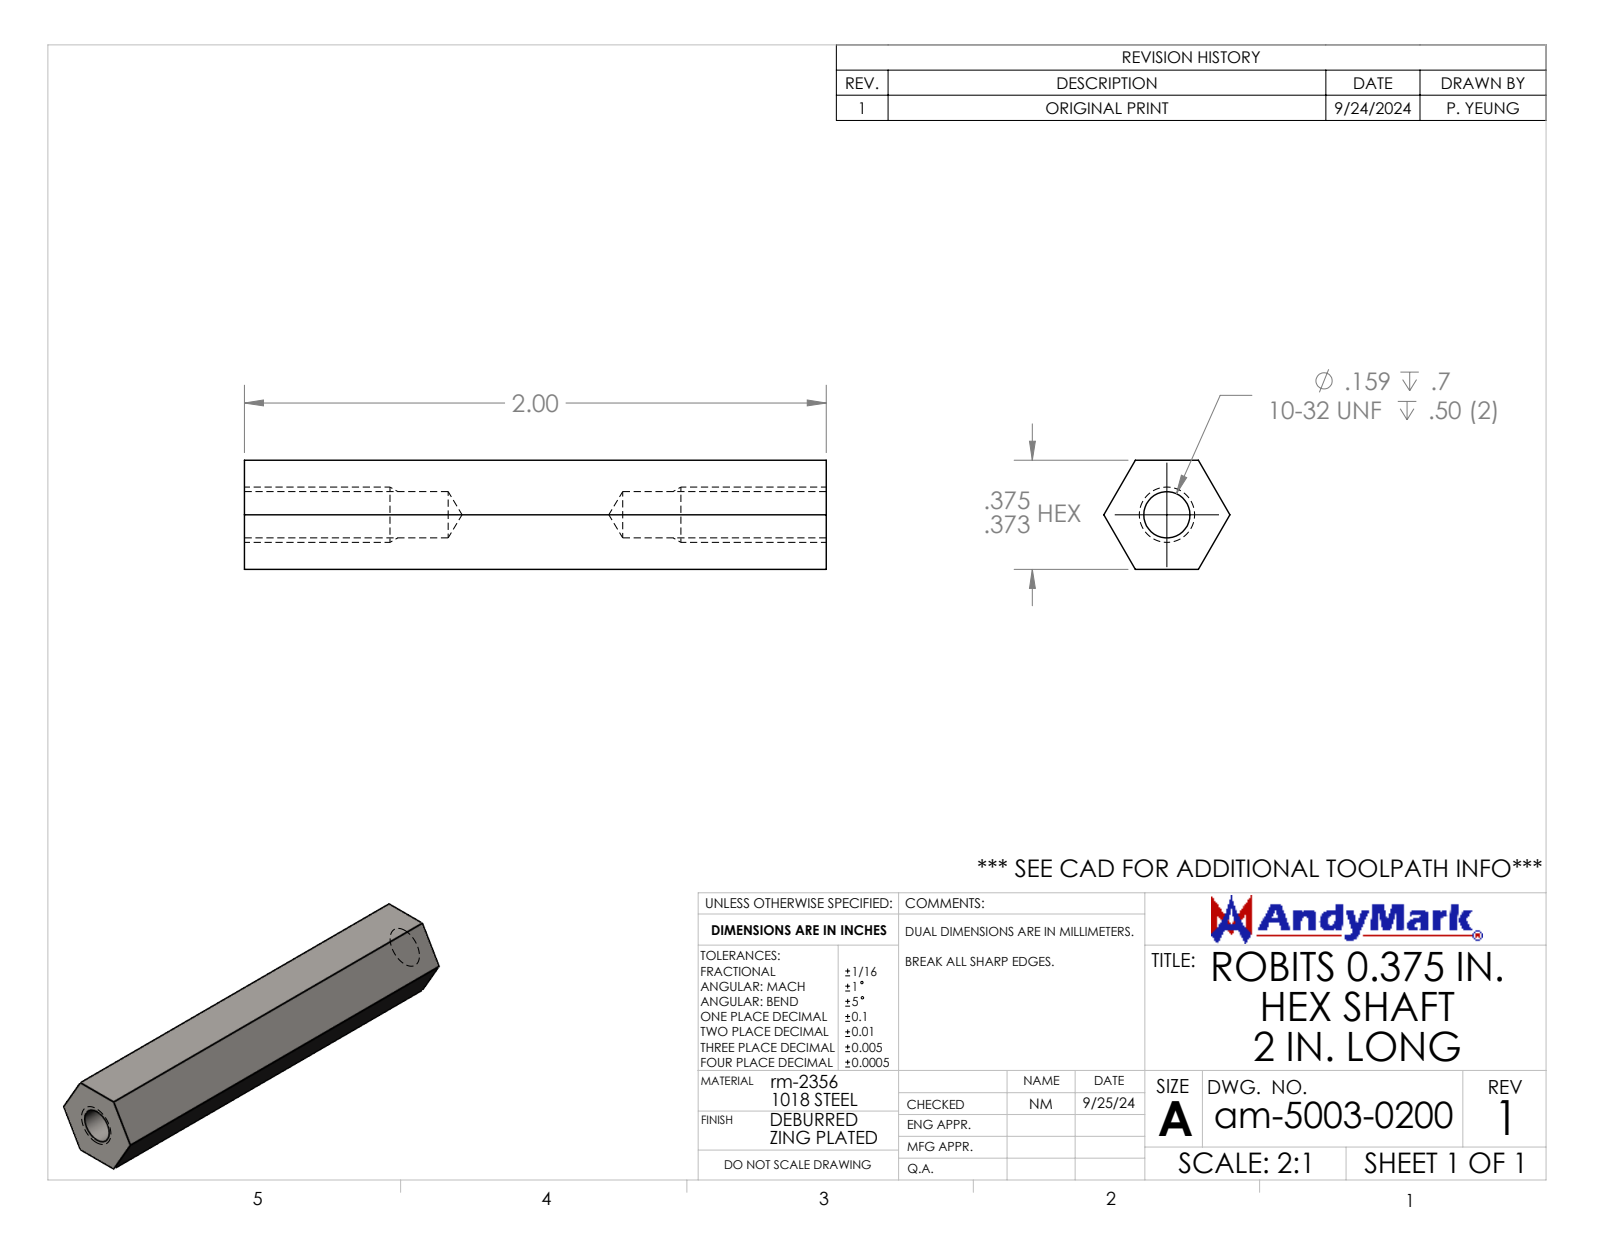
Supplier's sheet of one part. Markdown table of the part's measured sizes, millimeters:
| quantity | value |
| --- | --- |
| part name | am-5003-0200 Robits 0.375 in. Hex Shaft 2 in. Long |
| STEP written by | SolidWorks 2024 (AUTOMOTIVE_DESIGN) |
| units | millimeters |
| bodies | 1 solid, 16 faces (8 planar, 4 cylindrical, 4 other) |
| overall size | 50.8 × 11 × 9.5 |
| volume | 3 520 mm³ |
| surface area | 2 289 mm² |
| round holes (diameter × count) | 4 × 1 |
| main face-to-face distances | 9.5, 50.8 |
